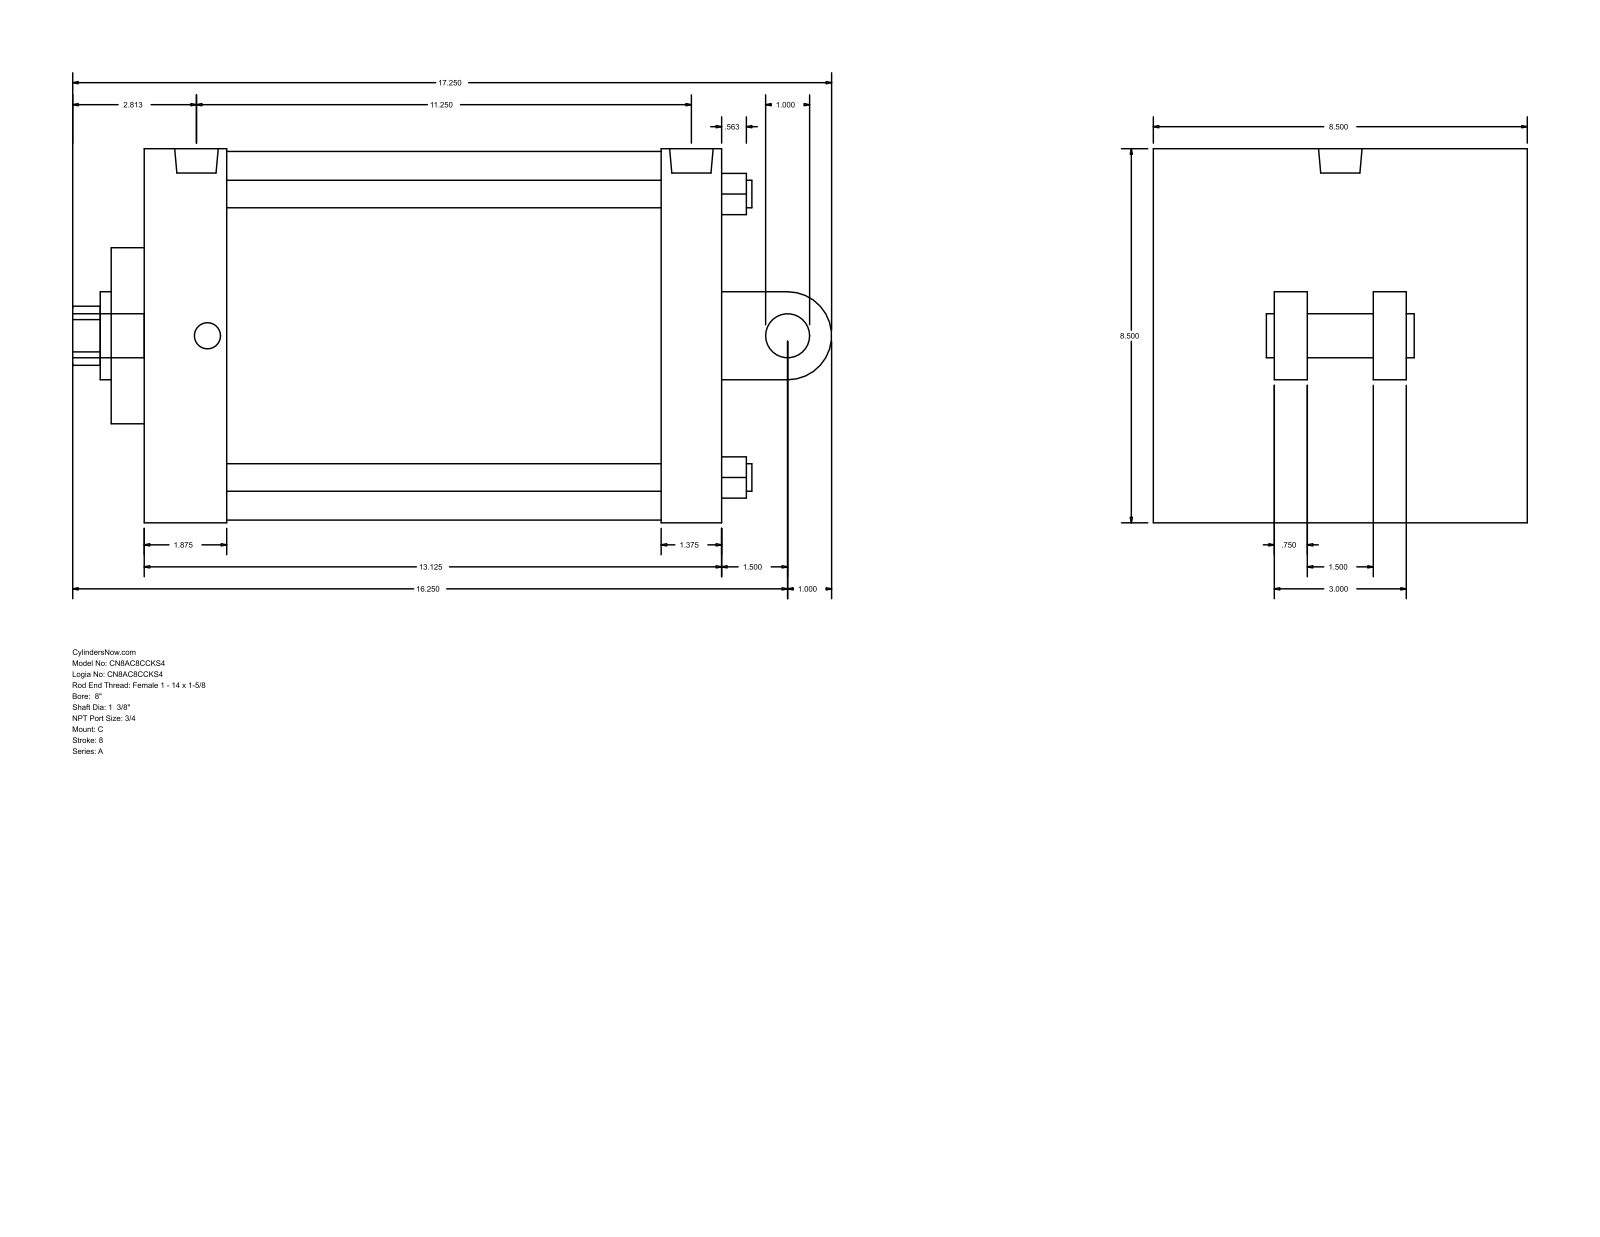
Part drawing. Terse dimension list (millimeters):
name: A_C__0800_1.375
written by: GSSL Pune (CONFIG_CONTROL_DESIGN)
unit: mm
bodies: 0 solids, 104 faces (75 planar, 29 cylindrical, 0 other)
size: 438.15 × 215.9 × 215.9
holes: 4× ⌀15.88, 2× ⌀15.08, 1× ⌀25.12, 1× ⌀34.92, 1× ⌀50.8, 1× ⌀212.72
bosses: 2× ⌀25.4, 2× ⌀15.08, 1× ⌀25.12
rounds: 1× R17.06, 1× R25.4
face distances: 333.38, 215.9, 57.15, 47.63, 285.75, 298.46, 250.83, 34.92, 88.9, 69.85
hole spacings: 115.67, 163.58, 231.34, 6.35
